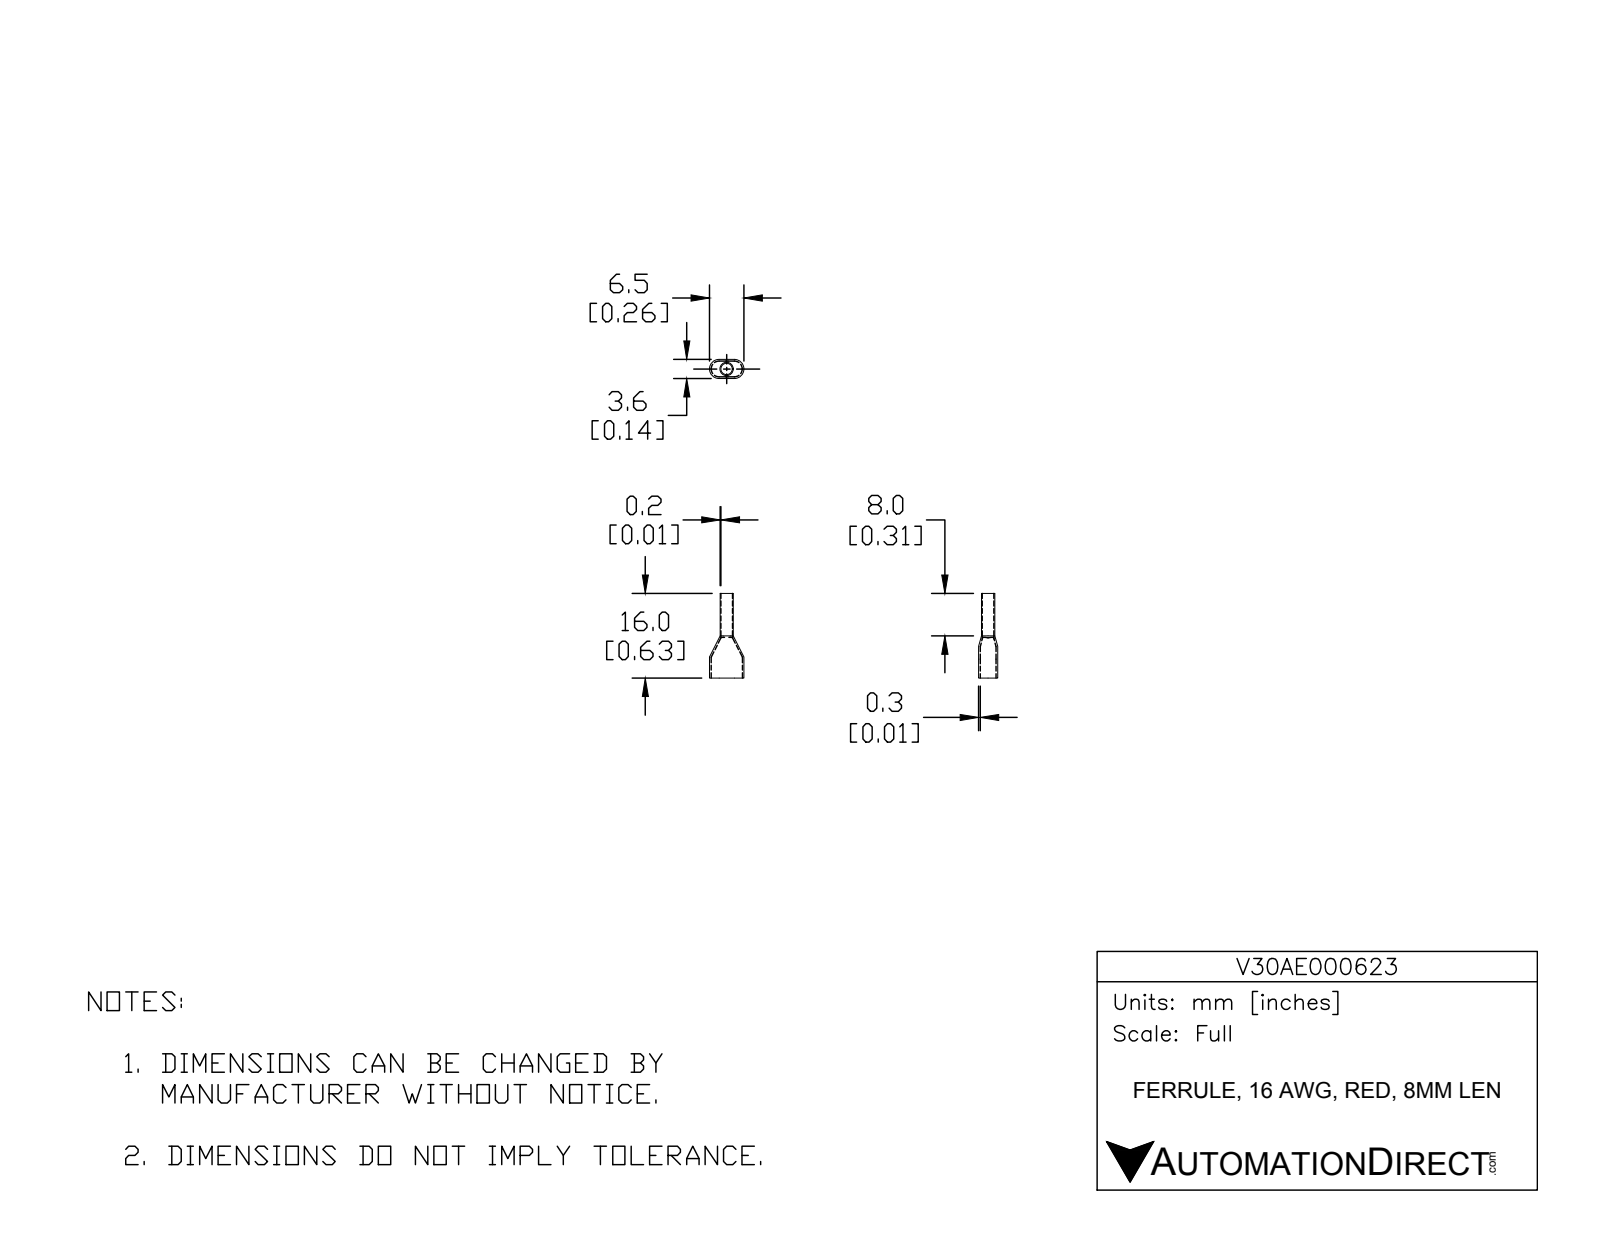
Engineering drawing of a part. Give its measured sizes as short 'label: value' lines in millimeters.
name: V30AE000623
written by: SolidWorks 2017 (AUTOMOTIVE_DESIGN)
unit: mm
bodies: 2 solids, 38 faces (16 planar, 22 cylindrical, 0 other)
size: 16 × 6.5 × 3.6
volume: 43 mm³; area: 356 mm²
holes: 1× ⌀2.2
bosses: 1× ⌀2.5
rounds: 4× R1.5, 4× R1.8
face distances: 3.3, 3.6, 3, 8, 16, 7.7, 8.3
